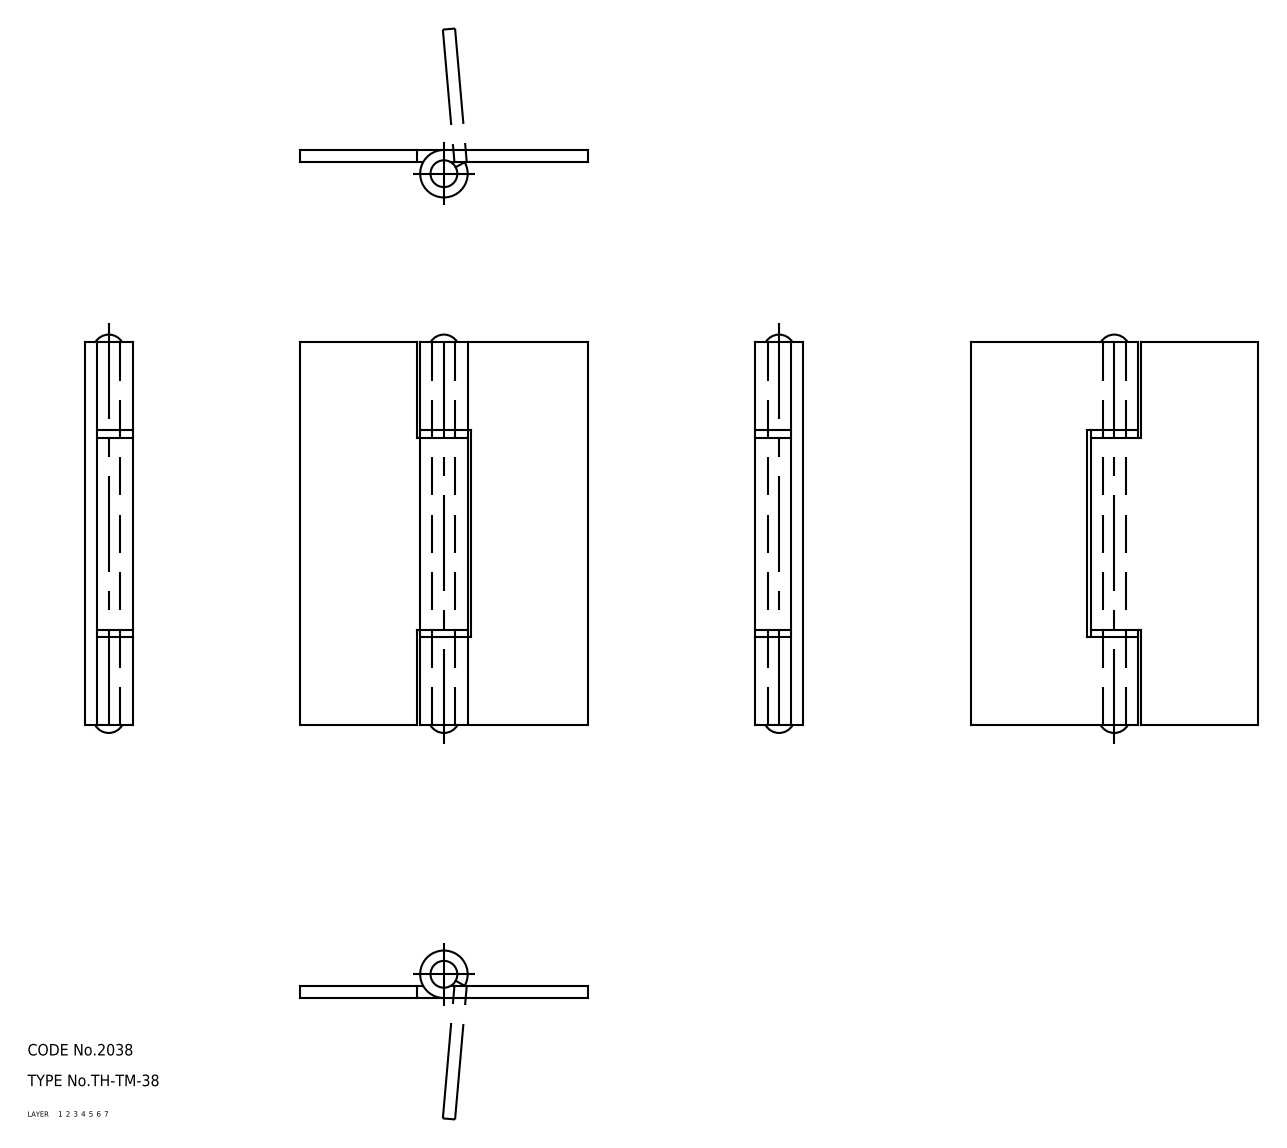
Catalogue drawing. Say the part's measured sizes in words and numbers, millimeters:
The part is named "washer; hinge piece_B; hinge piece_A; shaft (+1 more)". Its 3-D file was written by "CADfix (AUTOMOTIVE_DESIGN)". It is 5 solids with 44 faces: 0 planar, 0 cylindrical and 44 other. Overall it measures 103.96 by 75 by 12.4 millimeters. Its volume is 32 319 cubic millimeters and its surface area 23 019 square millimeters.
